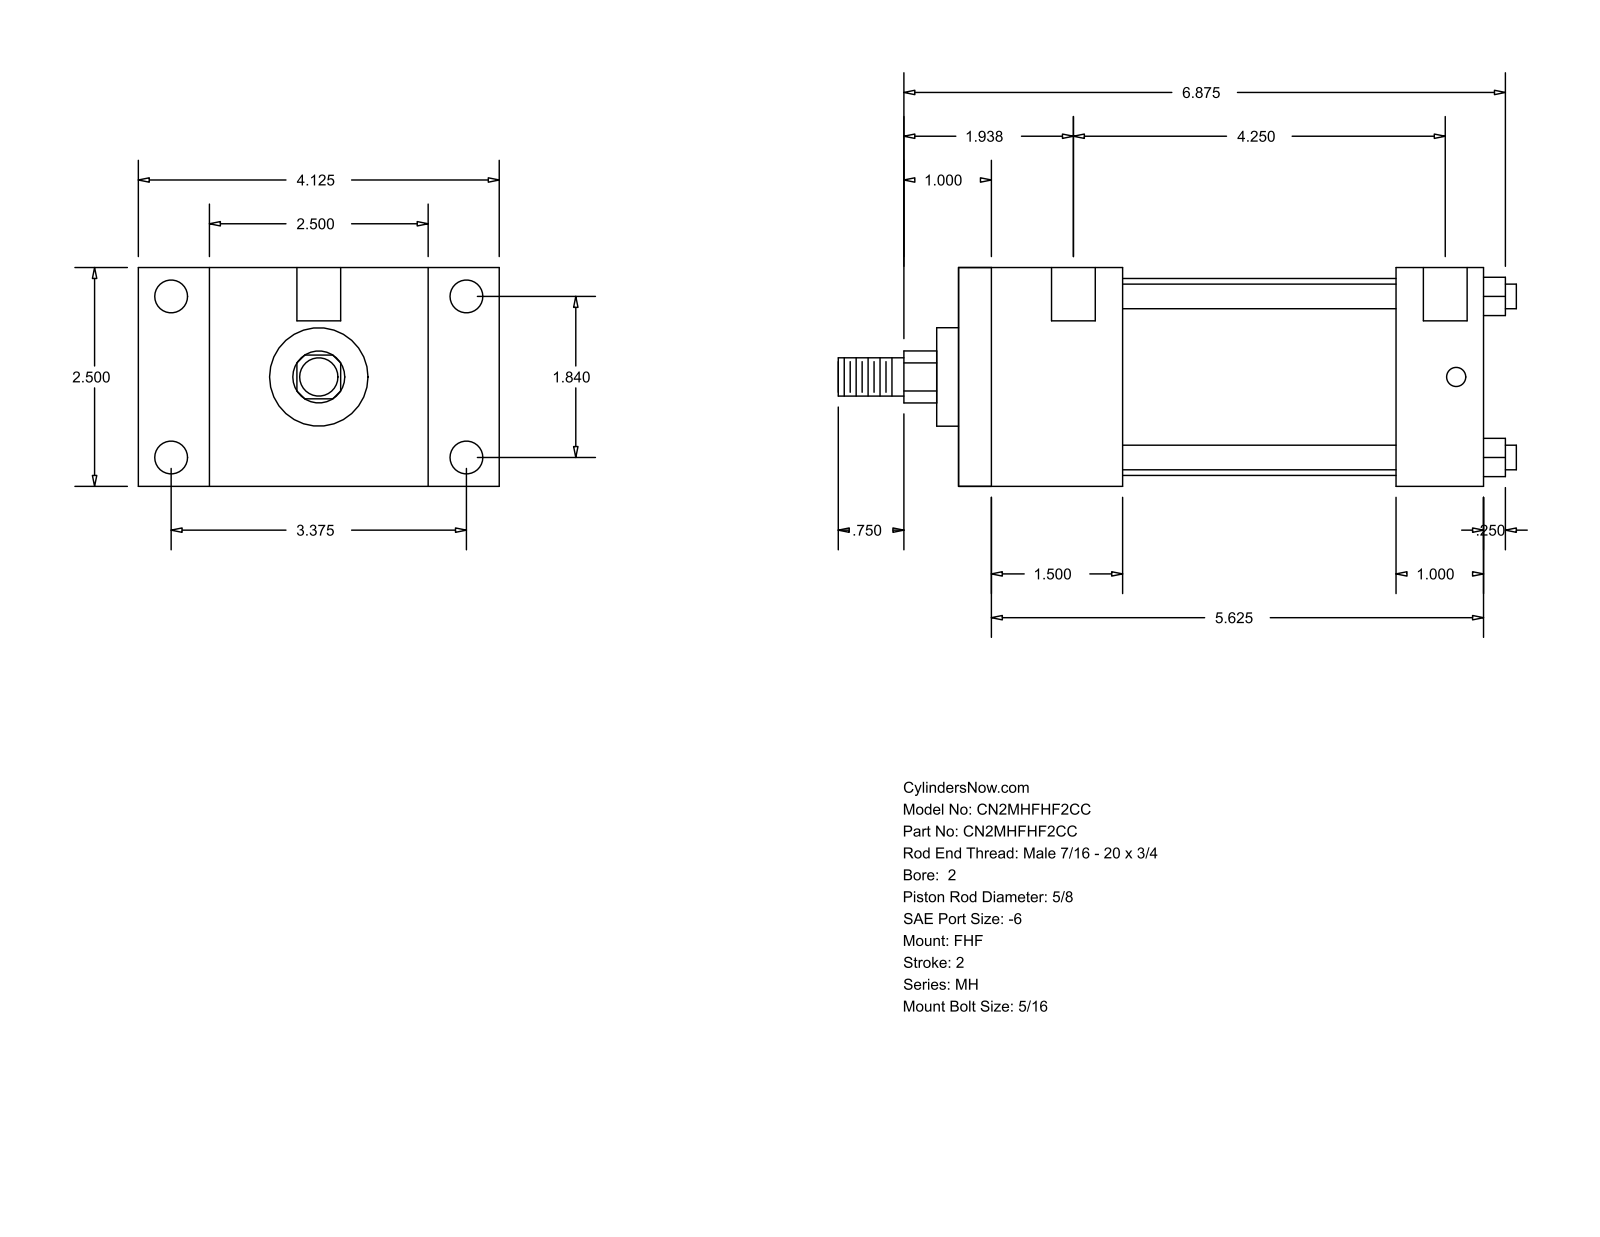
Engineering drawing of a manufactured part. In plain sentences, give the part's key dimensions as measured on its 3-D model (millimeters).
The part is named "MH_FHF__0200_0.625". Its 3-D file was written by "GSSL Pune (CONFIG_CONTROL_DESIGN)". It is 0 solids with 88 faces: 60 planar, 28 cylindrical and 0 other. Overall it measures 196.85 by 104.78 by 63.5 millimeters. Round holes: 4 of diameter 5.56, 4 of diameter 9.53, 2 of diameter 12.7. Round bosses or shafts: 4 of diameter 7.14, 1 of diameter 57.15, 1 of diameter 28.57, 1 of diameter 15.88, 1 of diameter 11.11. Partial cylindrical surfaces (rounded edges, fillets, slot ends): 1 of radius 7.54. The main face-to-face distances are 63.5, 104.78, 47.62, 152.4, 20.64, 84.14, 25.4, 127, 79.38, 6.35. The hole center spacings are 46.74, 85.72, 97.63, 115.89, 3.18, 4.76, 107.95, 111.13.
